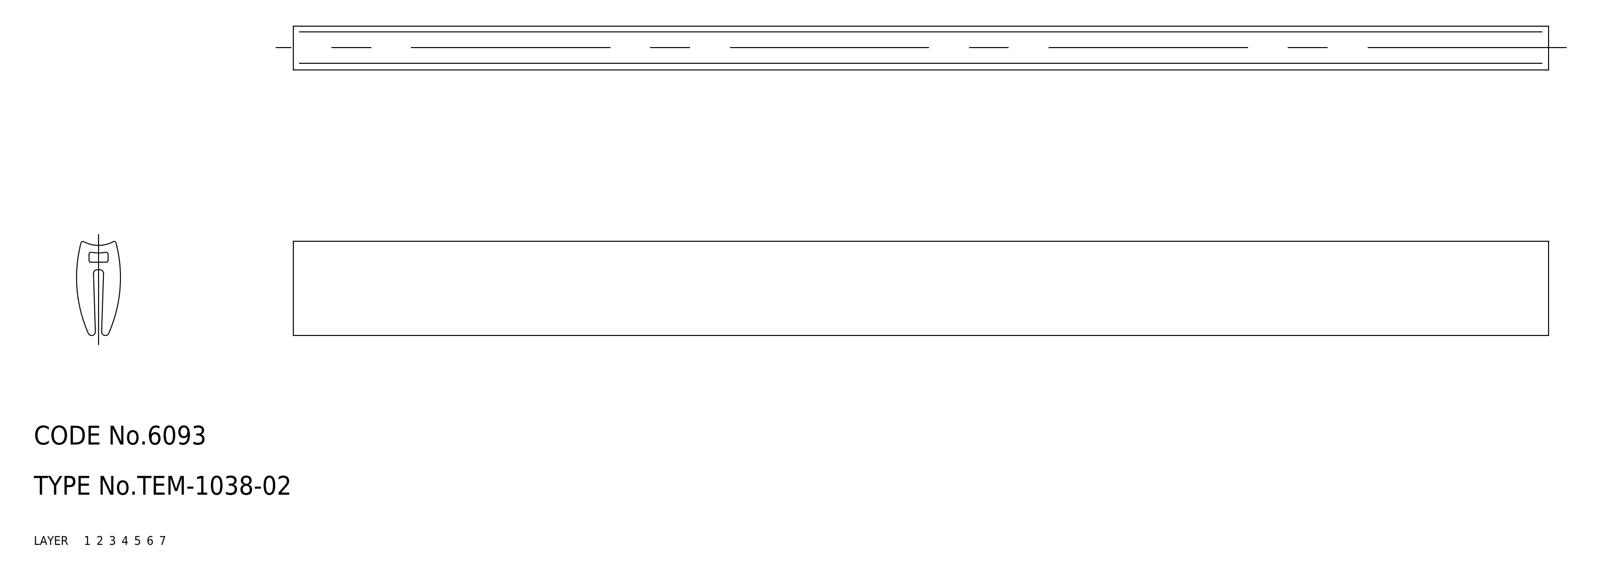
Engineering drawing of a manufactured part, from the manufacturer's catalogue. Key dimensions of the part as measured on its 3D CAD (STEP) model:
Part name (STEP PRODUCT): gasket
STEP written by: CADfix (AUTOMOTIVE_DESIGN)
Units: millimetres
Bodies: 1 solid, 22 faces (0 planar, 0 cylindrical, 22 other)
Overall size (bounding box): 200 × 15 × 7
Volume: 13 889 mm³ · Surface area: 13 806 mm²
